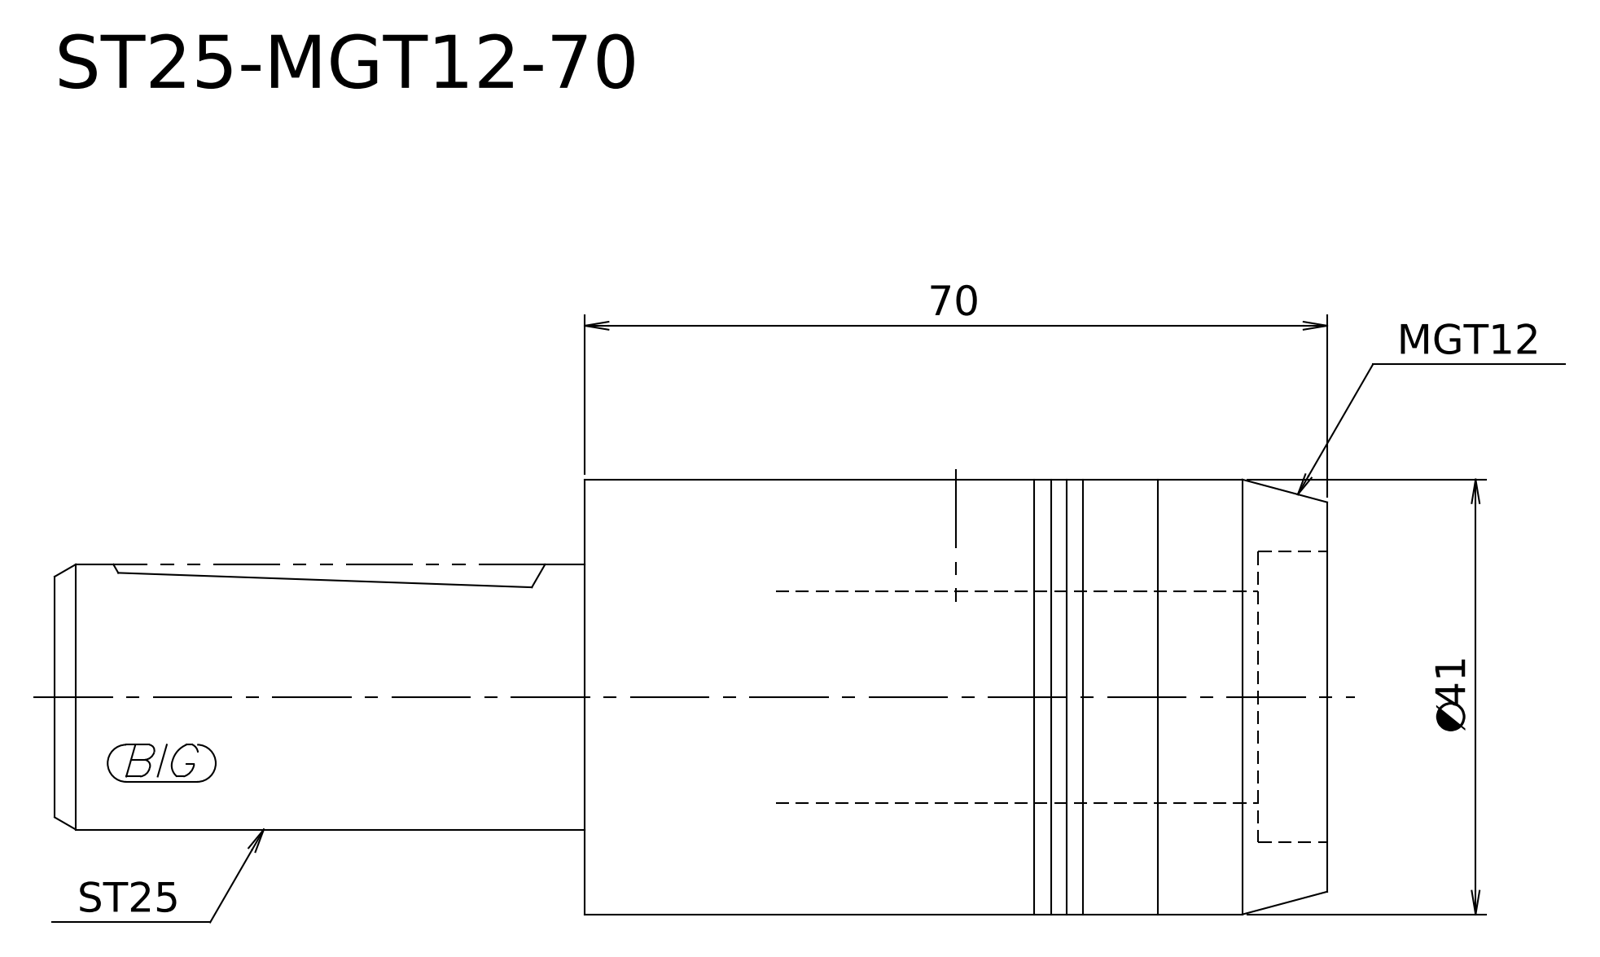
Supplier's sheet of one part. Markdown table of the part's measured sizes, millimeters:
| quantity | value |
| --- | --- |
| STEP written by | Kubotek KeyCreator V8.5.1 (14335) (CONFIG_CONTROL_DESIGN) |
| units | millimeters |
| bodies | 1 solid, 6 faces (3 planar, 2 cylindrical, 1 other) |
| overall size | 120 × 41 × 41 |
| volume | 115 896 mm³ |
| surface area | 15 303 mm² |
| round bosses / shafts (diameter × count) | 41 × 1, 25 × 1 |
| main face-to-face distances | 70, 120, 50 |
